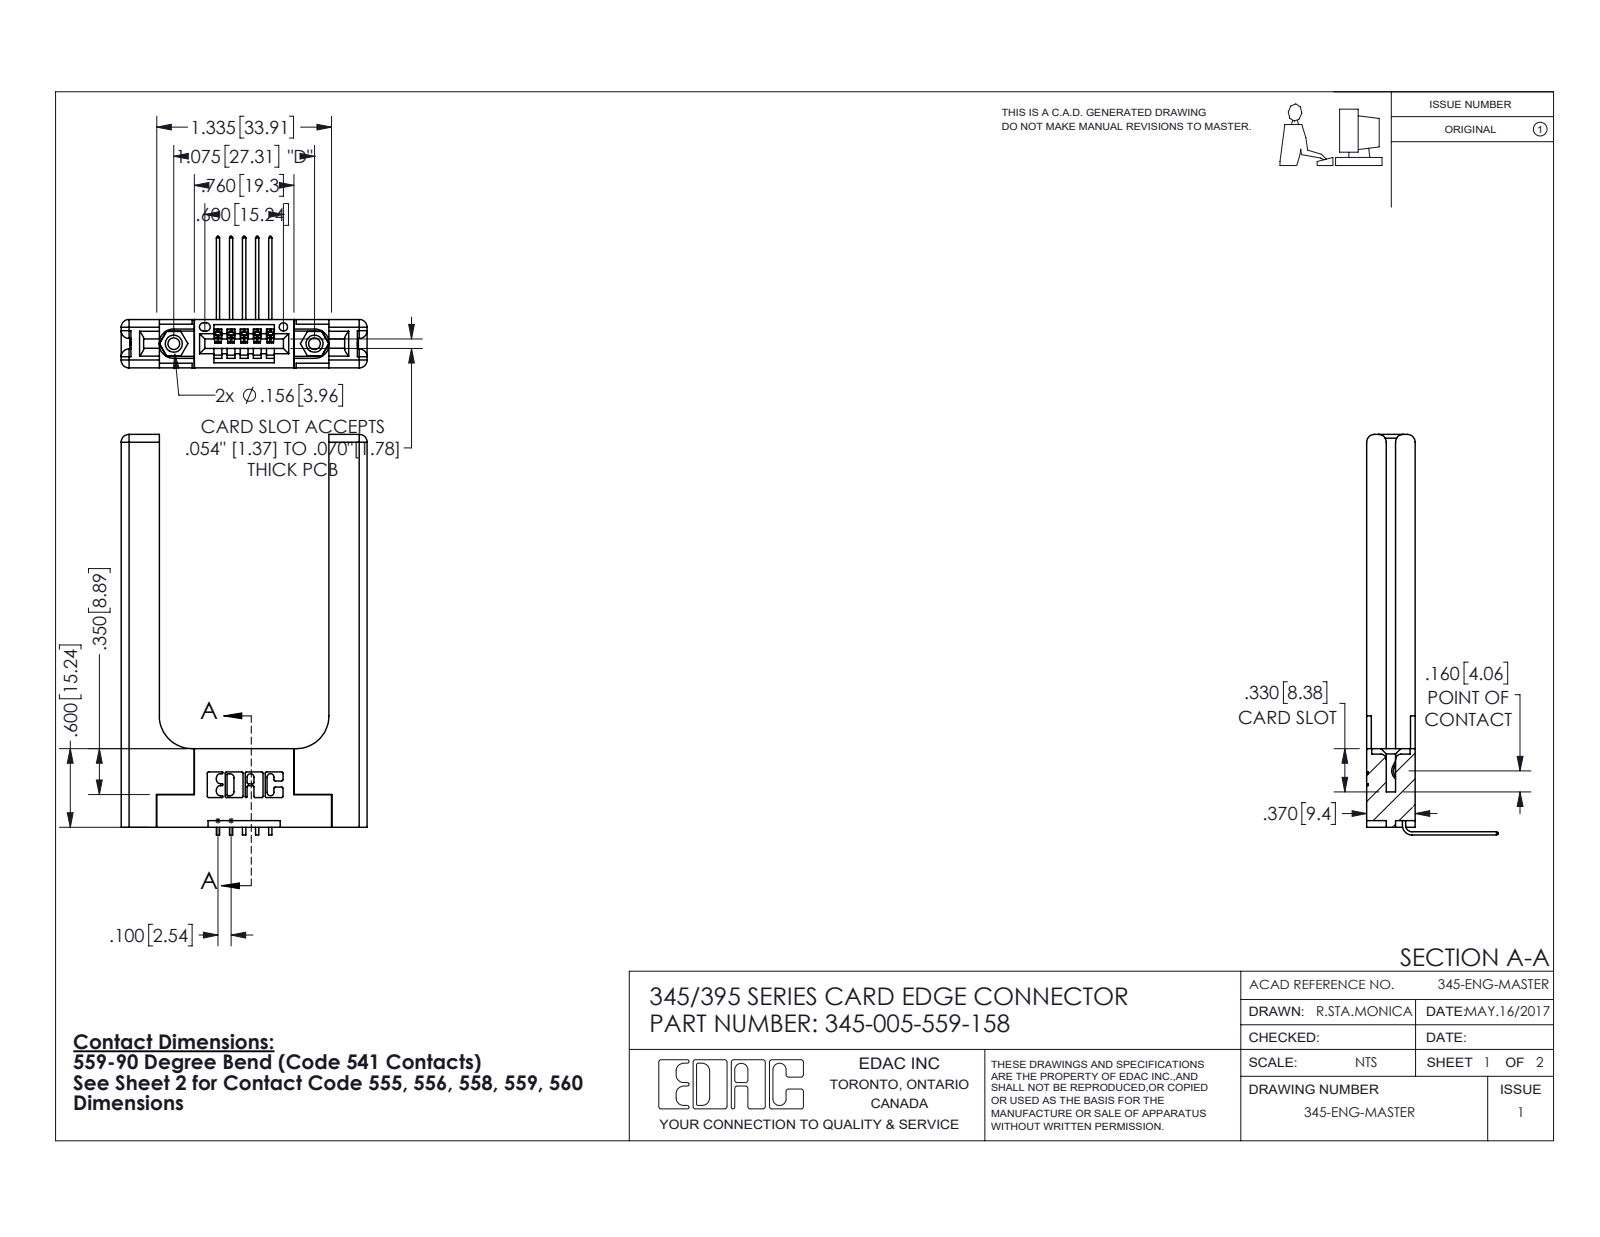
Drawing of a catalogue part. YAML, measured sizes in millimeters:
part_name: "345-220-058_345-220-058; 345-292-001_558 559 Tail - 1; 345 Part_Flush Mounting Lugs - 0.156 Dia-TH; 345-250-001_345-250-001-102 (+1 more)"
step_written_by: "SolidWorks 2016 (CONFIG_CONTROL_DESIGN)"
units: millimeters
bodies: {solids: 10, faces: 682, planar: 438, cylindrical: 184, other: 60}
overall_size: [77.7, 47.7, 25.5]
volume: 12700
surface_area: 10540
round_holes:
  - {diameter: 2.3, count: 2}
  - {diameter: 3.2, count: 2}
  - {diameter: 4, count: 2}
  - {diameter: 1.6, count: 1}
round_bosses_or_shafts:
  - {diameter: 3.9, count: 2}
partial_cylinders:
  - {radius: 0.3, count: 22}
  - {radius: 1.5, count: 16}
  - {radius: 0.2, count: 10}
  - {radius: 0.2, count: 6}
  - {radius: 0.8, count: 6}
  - {radius: 0.7, count: 3}
  - {radius: 0.8, count: 2}
  - {radius: 0.8, count: 2}
face_to_face_distances: [9.4, 3.8, 5.6, 1.8, 32.9, 1.8, 2, 3.8, 7.4, 40.3]
hole_center_spacings: [6.9, 21.5, 27.3]
